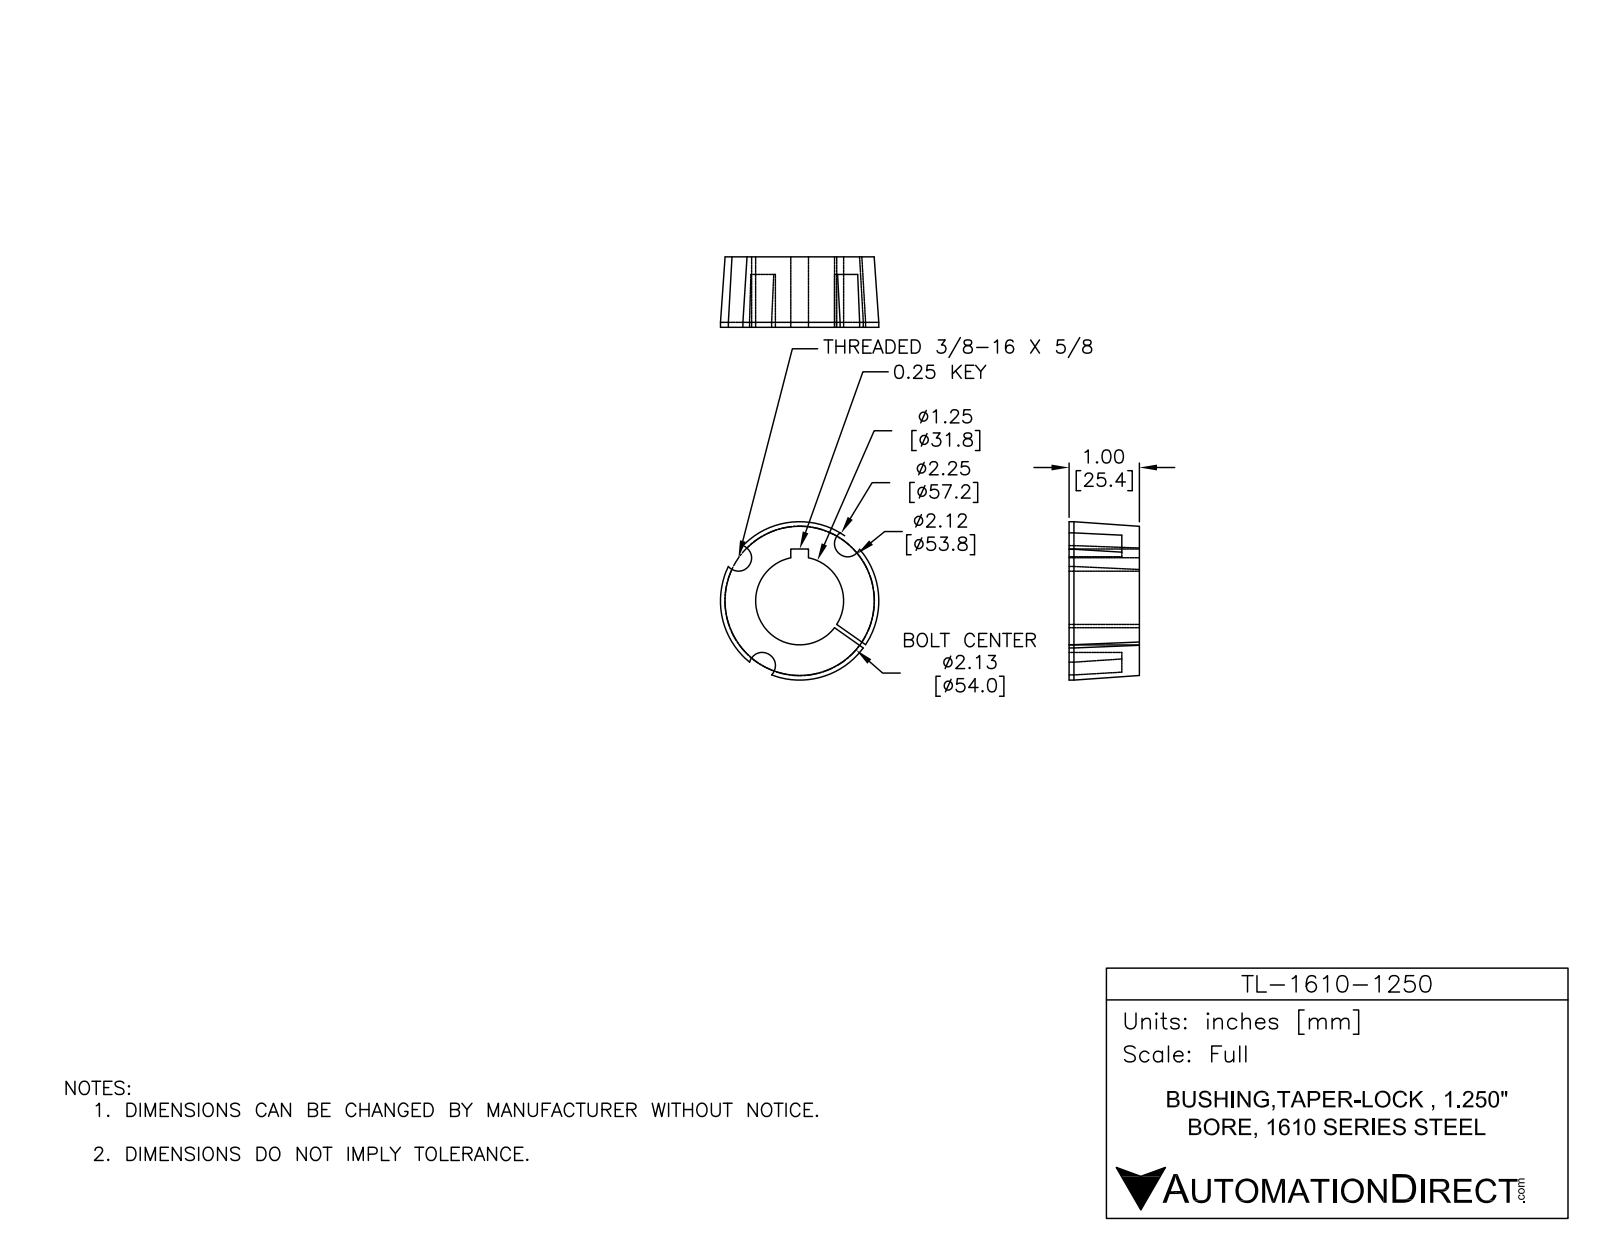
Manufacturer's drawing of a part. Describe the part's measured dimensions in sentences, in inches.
The part is named "TL-1610-1250". Its 3-D file was written by "SolidWorks 2014 (AUTOMOTIVE_DESIGN)". It is 1 solid with 25 faces: 9 planar, 13 cylindrical and 3 other. Overall it measures 2.25 by 2.25 by 1 inches. Its volume is 2.316 cubic inches and its surface area 17.32 square inches. Round holes: 1 of diameter 1.25. Round bosses or shafts: 1 of diameter 2.25. Partial cylindrical surfaces (rounded edges, fillets, slot ends): 3 of radius 0.188. The main face-to-face distances are 1, 0.057, 0.25, 0.75.
